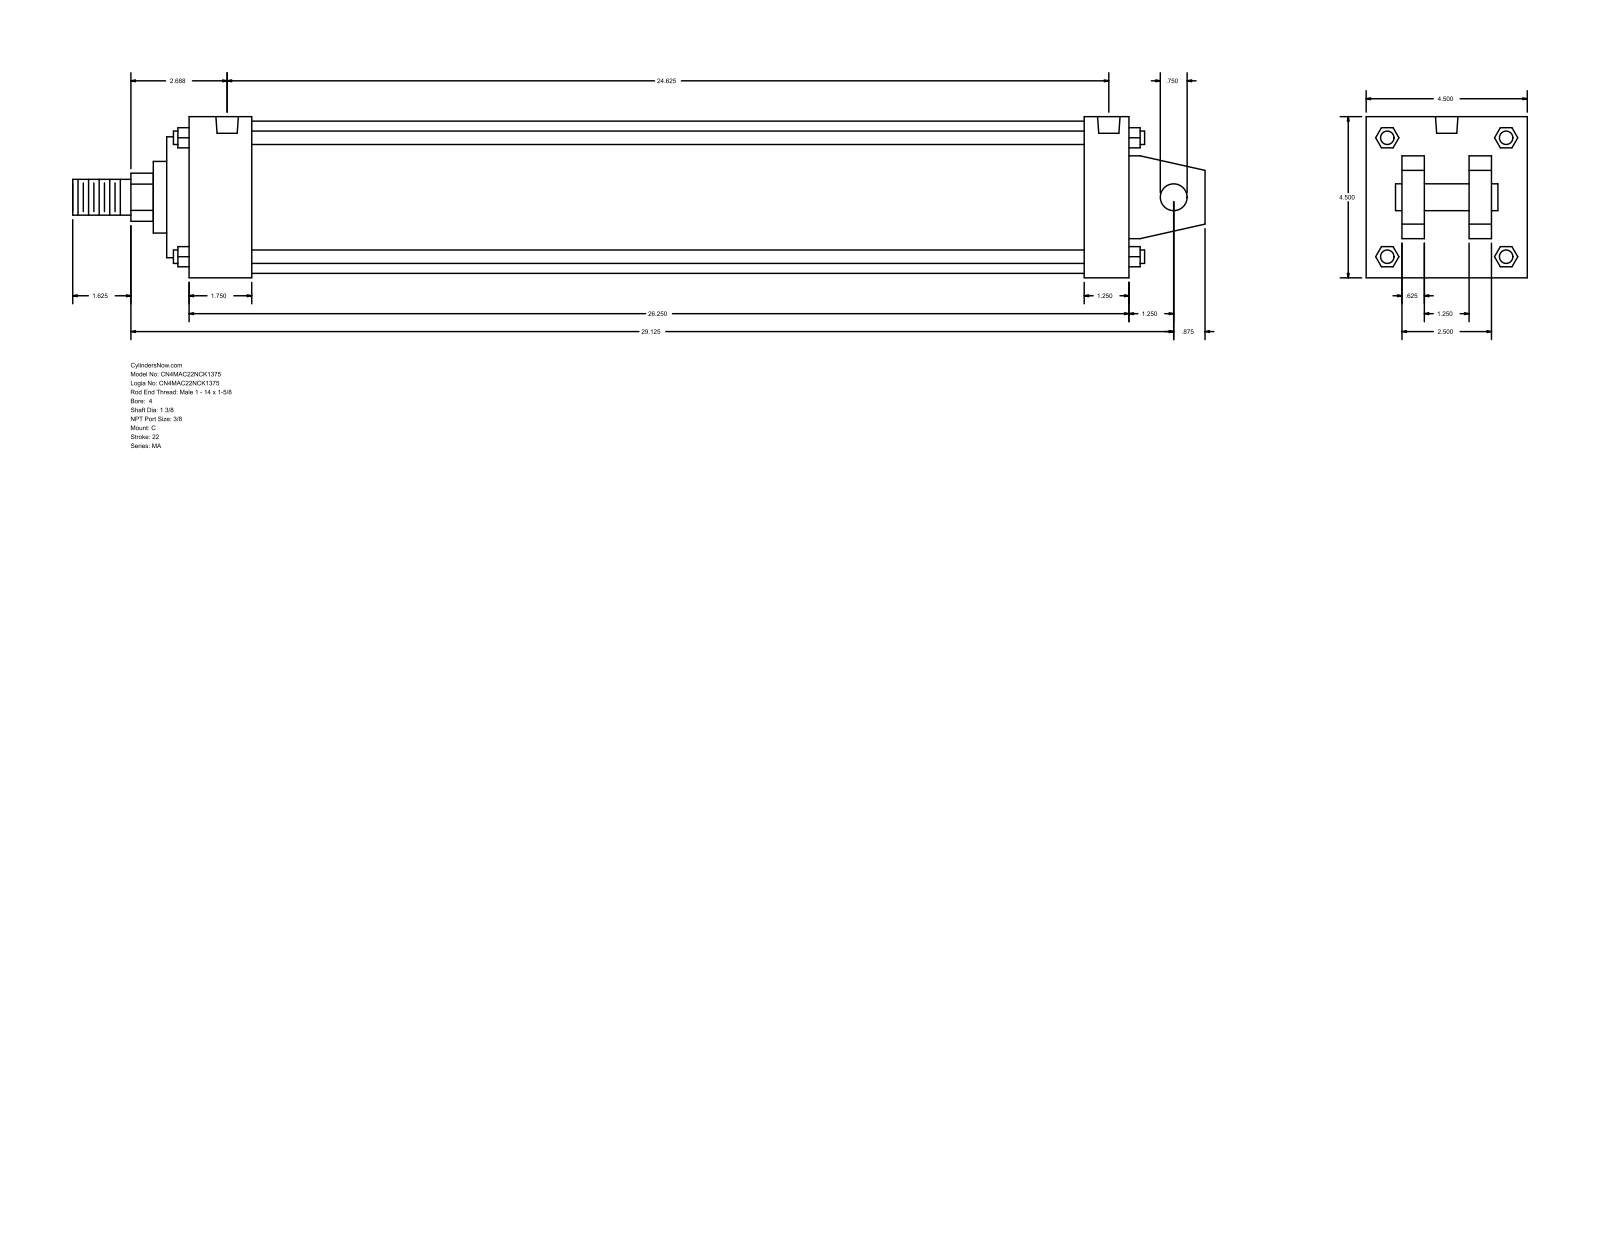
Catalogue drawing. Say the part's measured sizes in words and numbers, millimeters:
The part is named "MA_C__0400_1.375". Its 3-D file was written by "GSSL Pune (CONFIG_CONTROL_DESIGN)". It is 0 solids with 141 faces: 109 planar, 32 cylindrical and 0 other. Overall it measures 803.27 by 114.3 by 114.3 millimeters. Round holes: 4 of diameter 11.11, 2 of diameter 15.93. Round bosses or shafts: 4 of diameter 9.53, 1 of diameter 107.95, 1 of diameter 85.72, 1 of diameter 50.8, 1 of diameter 34.92, 1 of diameter 25.4, 1 of diameter 19.05. Partial cylindrical surfaces (rounded edges, fillets, slot ends): 1 of radius 17.06. The main face-to-face distances are 114.3, 15.87, 666.75, 73.03, 41.27, 25.4, 88.9, 47.63, 682.62, 650.87. The hole center spacings are 615.95, 4.76, 4.77, 620.71, 620.72, 625.48.
